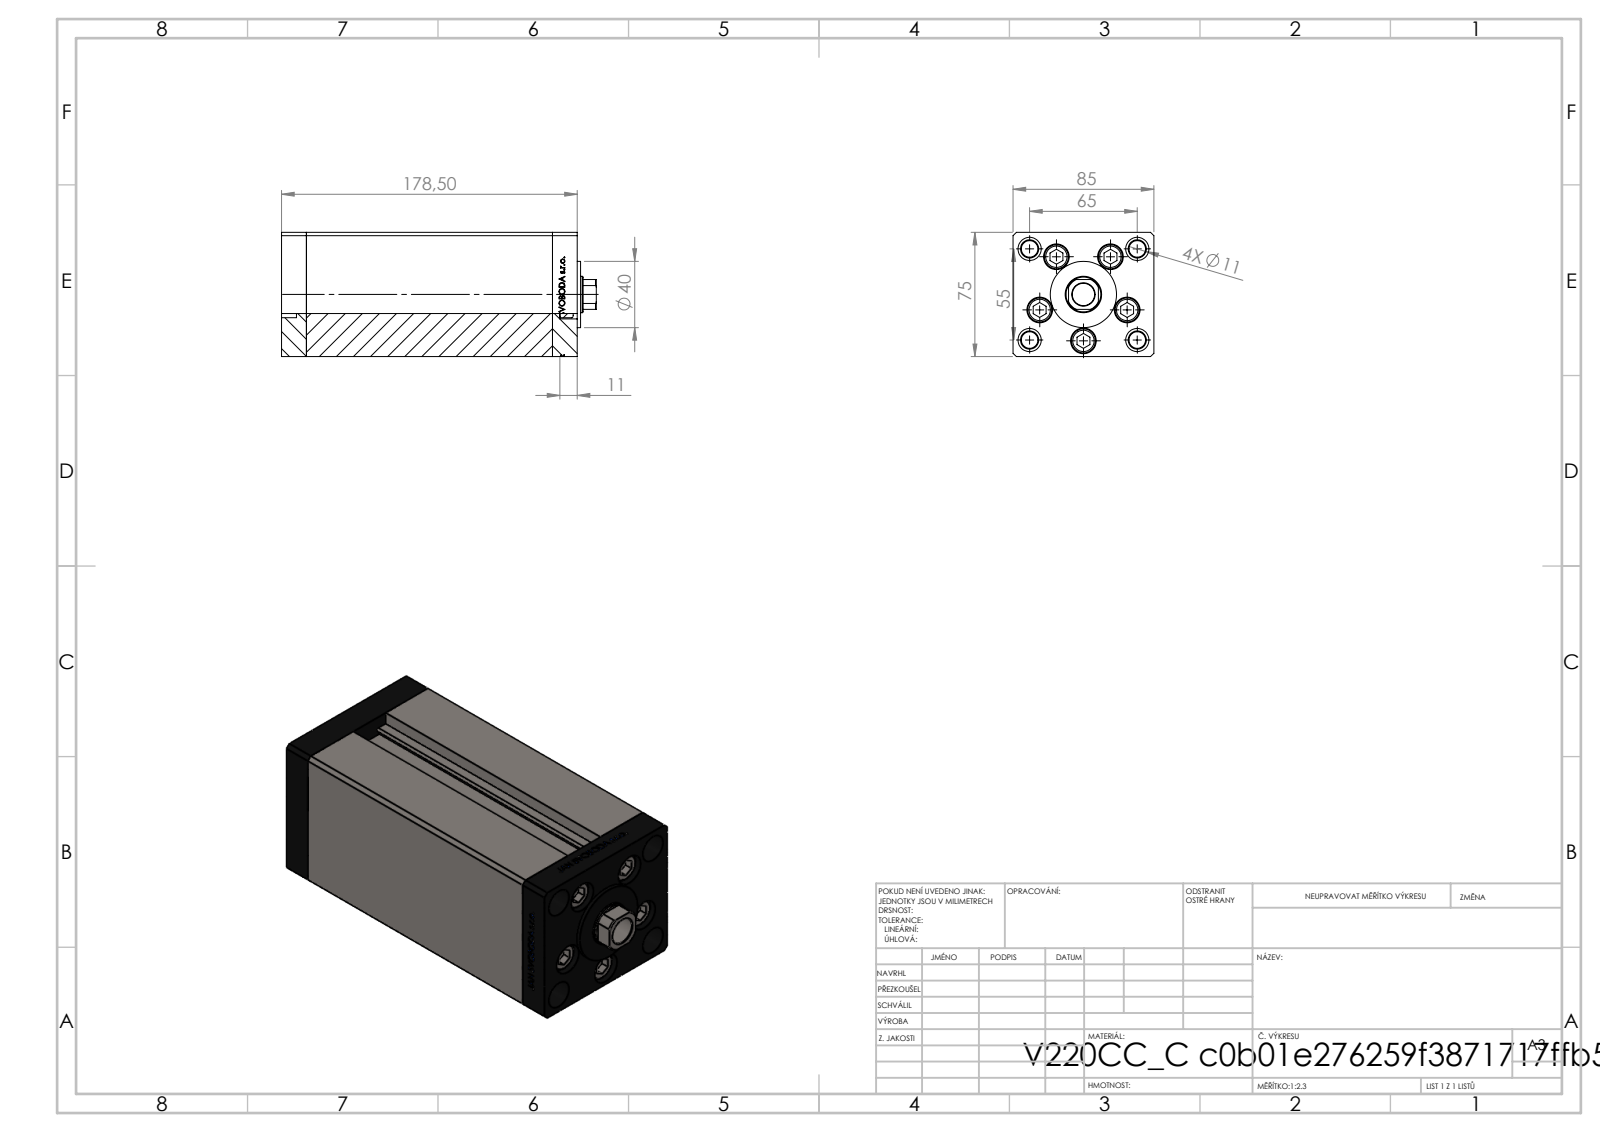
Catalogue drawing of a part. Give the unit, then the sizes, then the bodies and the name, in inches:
Units: inches
Overall size (bounding box): 7.48 × 3.346 × 2.953
Round holes (diameter × count): ⌀0.433 ×9, ⌀0.61 ×5, ⌀0.394 ×4, ⌀0.551 ×4, ⌀0.531 ×1, ⌀0.571 ×1, ⌀0.866 ×1
Round bosses / shafts (diameter × count): ⌀0.315 ×5, ⌀0.571 ×4, ⌀1.575 ×1
Partial cylindrical surfaces — rounded edges, fillets, slot ends (radius × count): R0.037 ×2, R0.413 ×1
Main face-to-face distances: 3.346, 2.953, 0.591, 5.846, 6.437, 0.413, 7.028, 1.348, 5.679, 5.089
Hole centre spacings: 1.102, 1.676, 0.664, 0.755, 1.273, 1.28, 1.324, 1.47
Volume: 57.91 in³ · Surface area: 277.8 in²
Bodies: 13 solids, 1159 faces (538 planar, 159 cylindrical, 462 other)
Part name (STEP PRODUCT): ALLEN BOLT; V220C_C MIDDLE; V220C FRONT; V220C_VC_C (+1 more)
STEP written by: SolidWorks 2019 (CONFIG_CONTROL_DESIGN)
